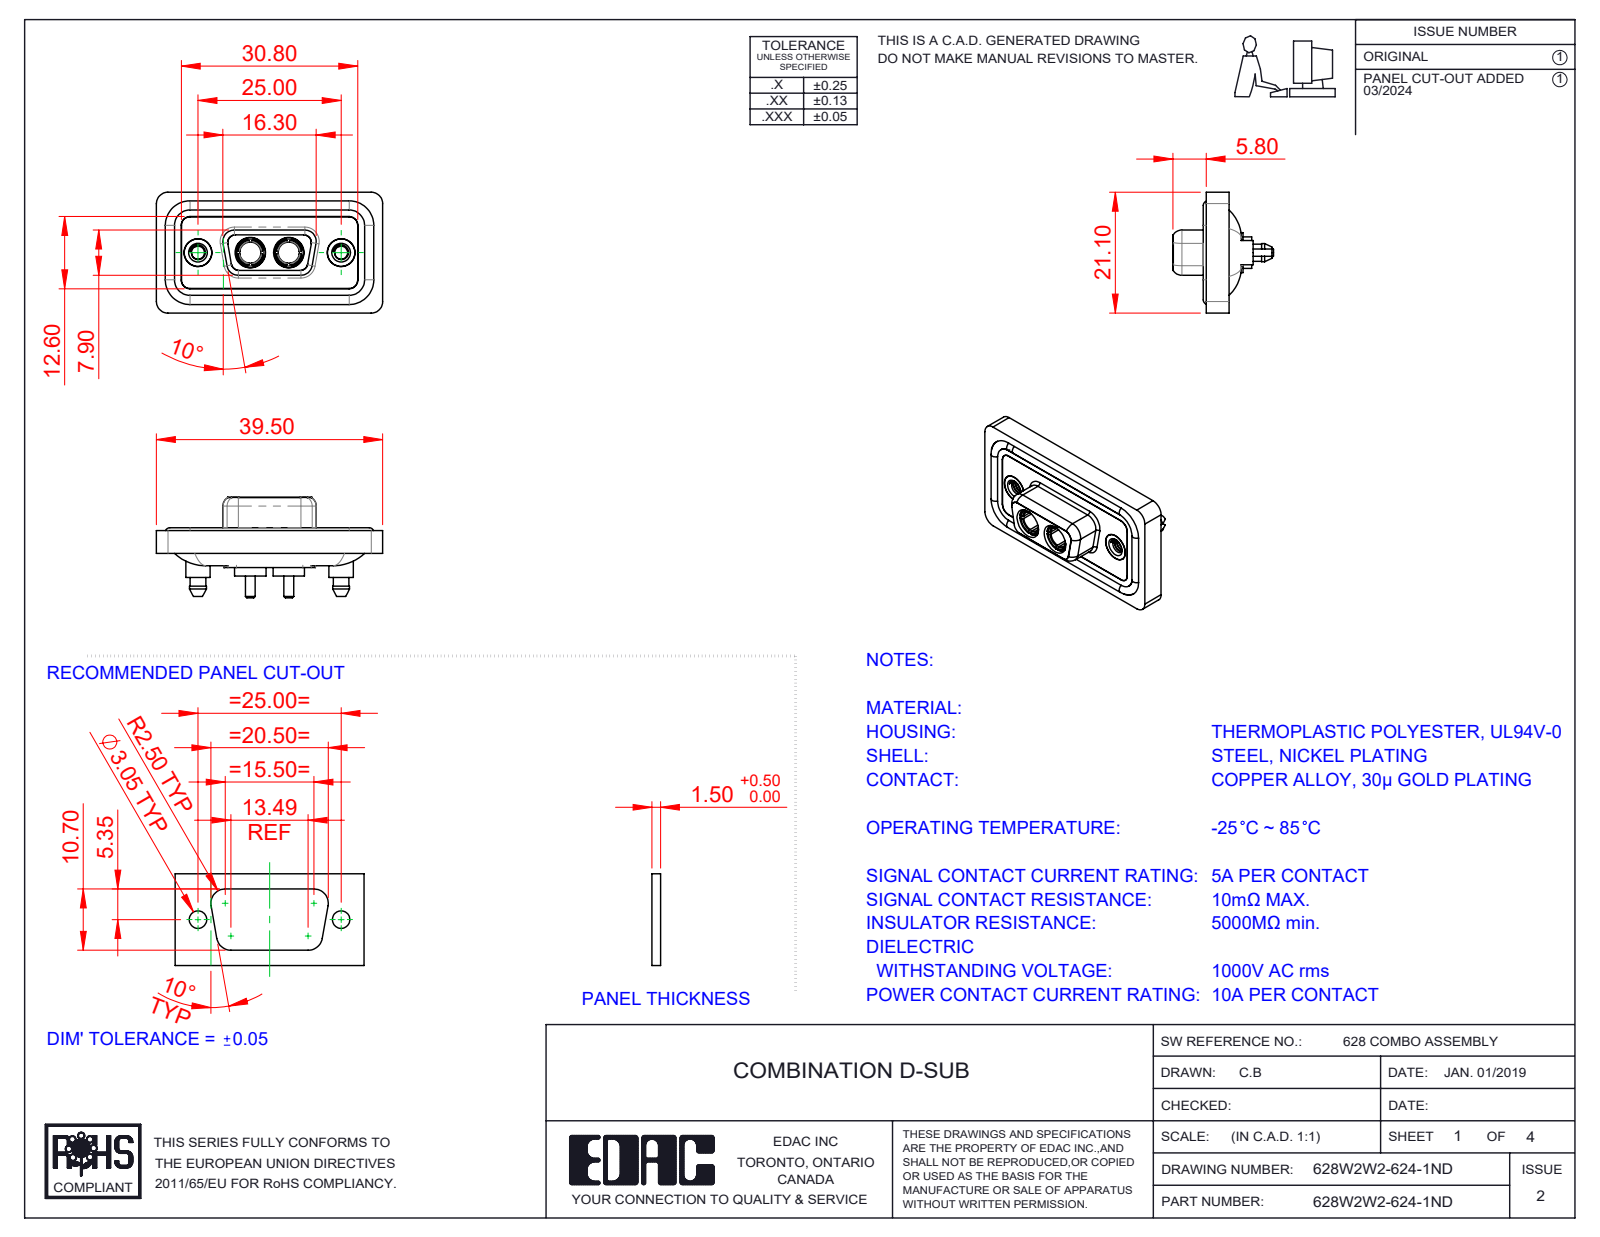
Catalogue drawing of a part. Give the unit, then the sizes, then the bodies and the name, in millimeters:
Units: millimetres
Overall size (bounding box): 39.5 × 21.1 × 17.55
Round holes (diameter × count): ⌀4.85 ×4, ⌀2.26 ×2, ⌀3.7 ×2, ⌀4 ×2, ⌀4.05 ×2, ⌀5 ×2, ⌀5.3 ×2
Round bosses / shafts (diameter × count): ⌀1.6 ×4, ⌀5.5 ×2, ⌀5.4 ×2, ⌀5.2 ×2, ⌀4.96 ×2, ⌀4.95 ×2, ⌀4.8 ×2, ⌀4.75 ×2
Partial cylindrical surfaces — rounded edges, fillets, slot ends (radius × count): R1.5 ×24, R2 ×18, R1.6 ×10, R1.35 ×8, R0.25 ×4, R0.5 ×4, R0.6 ×4, R0.65 ×4
Main face-to-face distances: 0.4, 1.8, 1.1, 2.9, 1.6, 0.5, 5.65, 1.5, 7.45, 4
Hole centre spacings: 9.14, 15.86, 6.72, 25
Volume: 4 819 mm³ · Surface area: 7 950 mm²
Bodies: 11 solids, 600 faces (179 planar, 282 cylindrical, 139 other)
Part name (STEP PRODUCT): 628Combo Shell Rear_09 Contacts; 628Combo Housing_2W2; Power Socket_10A S; 628Combo Shell Front_09 Contacts (+3 more)
STEP written by: SolidWorks 2023 (CONFIG_CONTROL_DESIGN)
